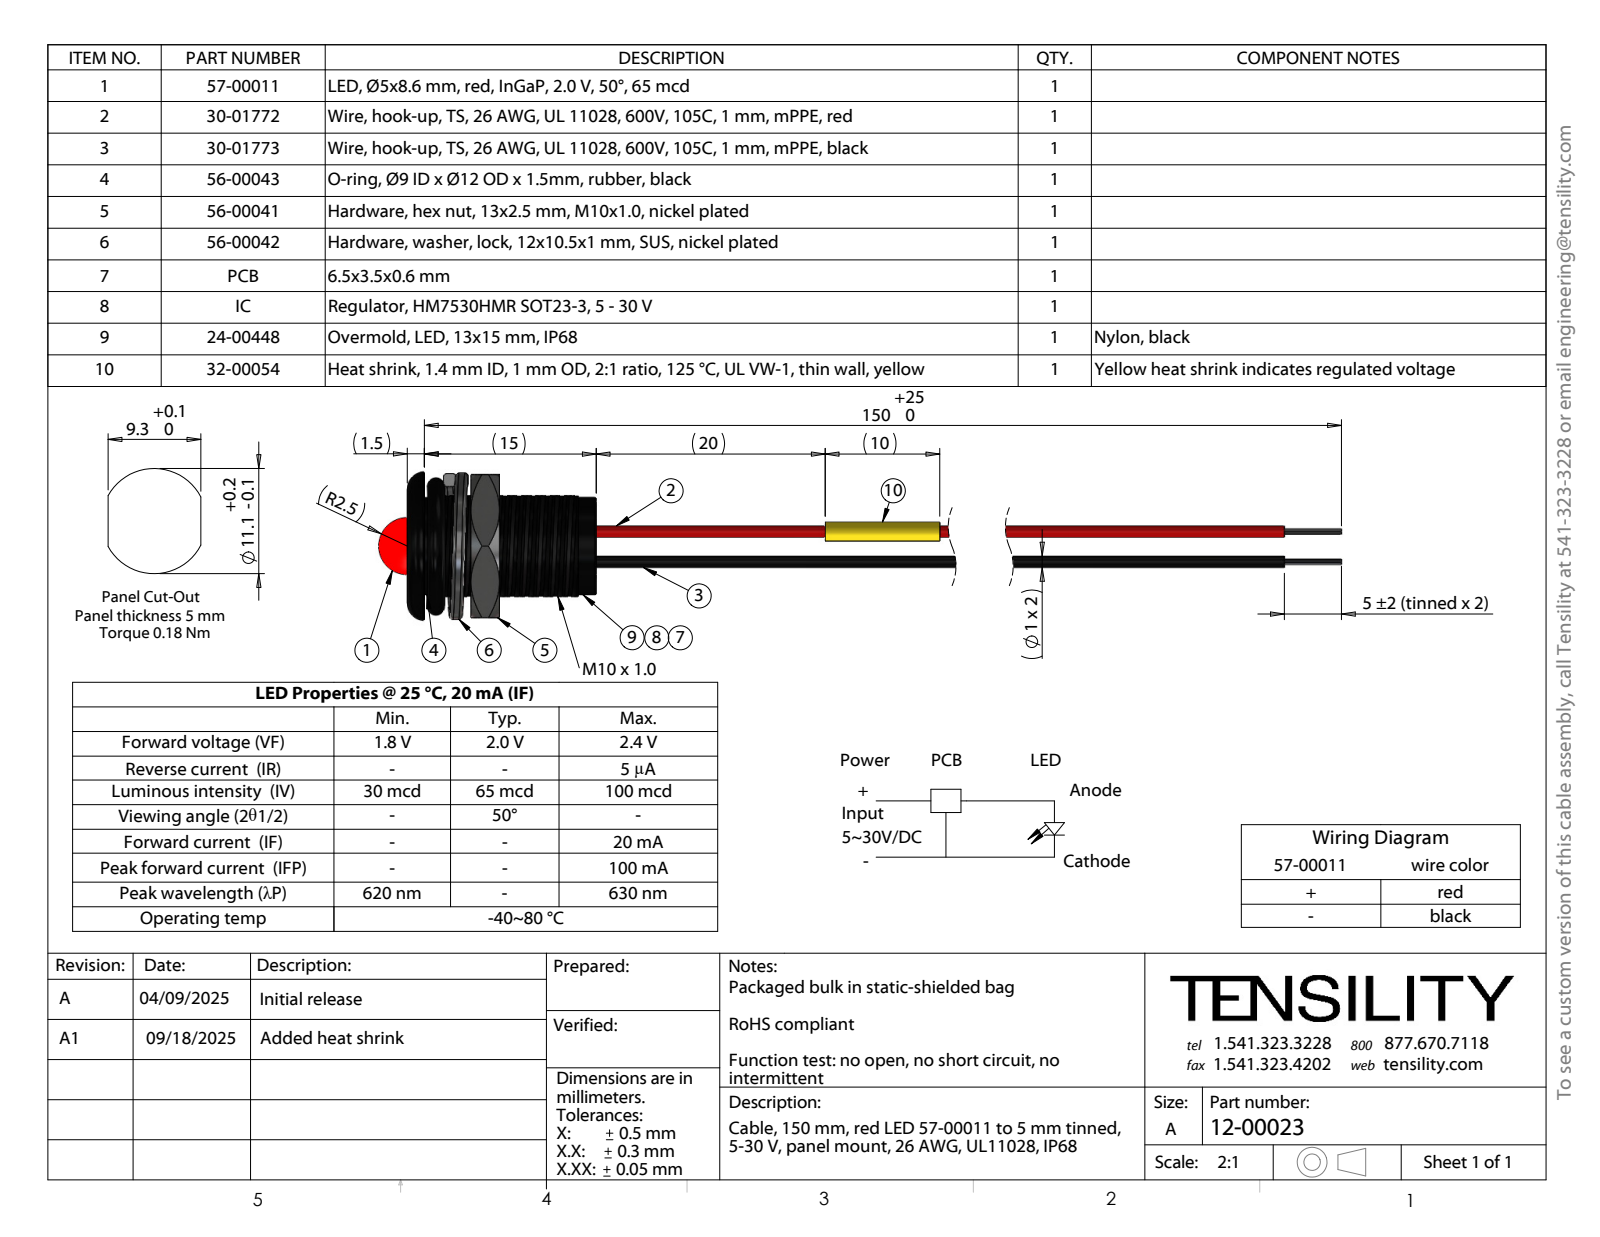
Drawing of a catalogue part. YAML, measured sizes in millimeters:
part_name: "57-00011_trimmed leads; 24-00448; 56-00042_Split washer; 12-00023_revA (+4 more)"
step_written_by: "SolidWorks 2021 (CONFIG_CONTROL_DESIGN)"
units: millimeters
bodies: {solids: 57, faces: 514, planar: 185, cylindrical: 246, other: 83}
overall_size: [173.99, 14.43, 12.99]
volume: 1769
surface_area: 6568
round_holes:
  - {diameter: 1, count: 2}
round_bosses_or_shafts:
  - {diameter: 1, count: 2}
  - {diameter: 0.83, count: 2}
  - {diameter: 8.5, count: 1}
  - {diameter: 5, count: 1}
partial_cylinders:
  - {radius: 4.33, count: 1}
  - {radius: 5, count: 1}
face_to_face_distances: [1.5, 16.5, 15, 12.5, 8.06, 6.56, 8.44, 5.56, 4.06, 2.5]
hole_center_spacings: [0.36, 0.38, 0.33, 2.43, 2.35, 2.48, 2.52, 2.56]
